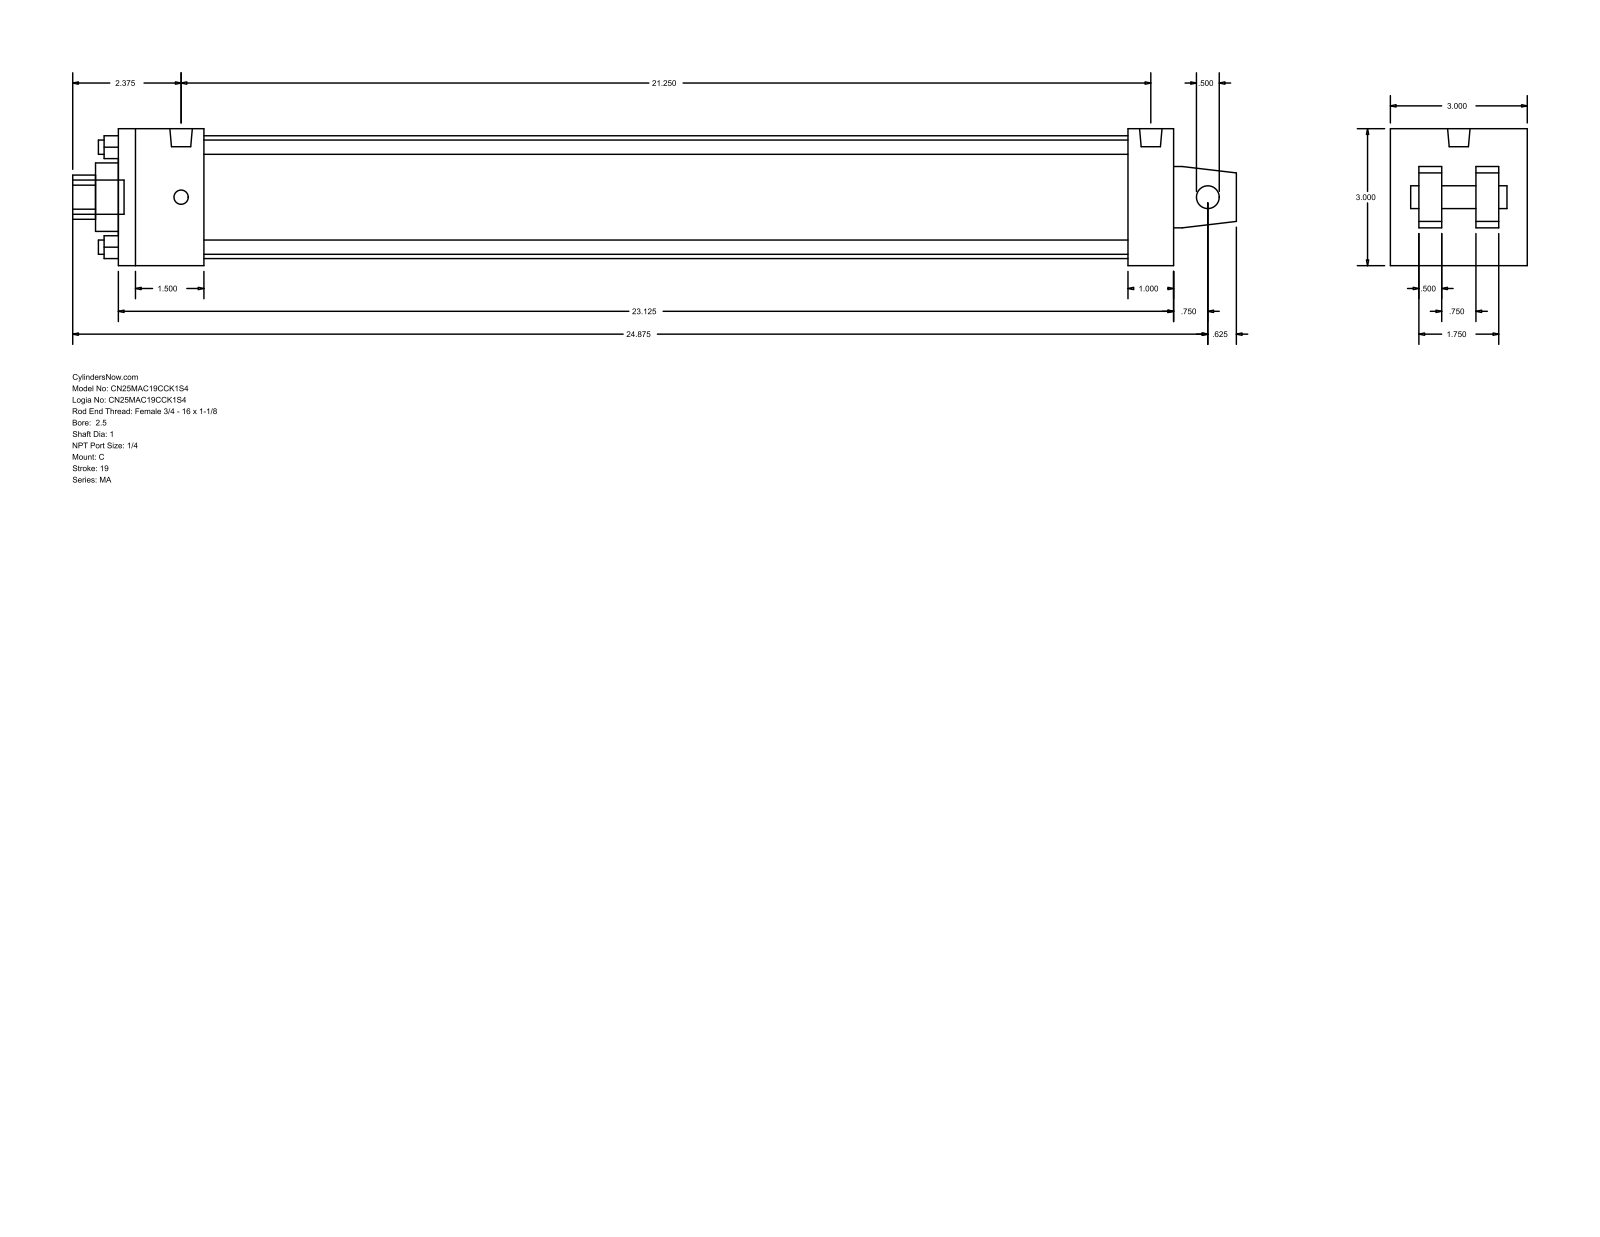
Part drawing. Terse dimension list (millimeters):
name: MA_C__0250_1
written by: GSSL Pune (CONFIG_CONTROL_DESIGN)
unit: mm
bodies: 0 solids, 103 faces (76 planar, 27 cylindrical, 0 other)
size: 647.7 × 76.2 × 76.2
holes: 4× ⌀7.94, 1× ⌀12.7, 1× ⌀25.4, 1× ⌀38.1, 1× ⌀68.33
bosses: 4× ⌀7.94, 2× ⌀12.49, 1× ⌀19.05
rounds: 1× R12.29
face distances: 76.2, 47.63, 587.37, 12.7, 15.87, 60.33, 28.57, 561.98, 514.35, 539.74
hole spacings: 39.33, 55.62, 78.66
